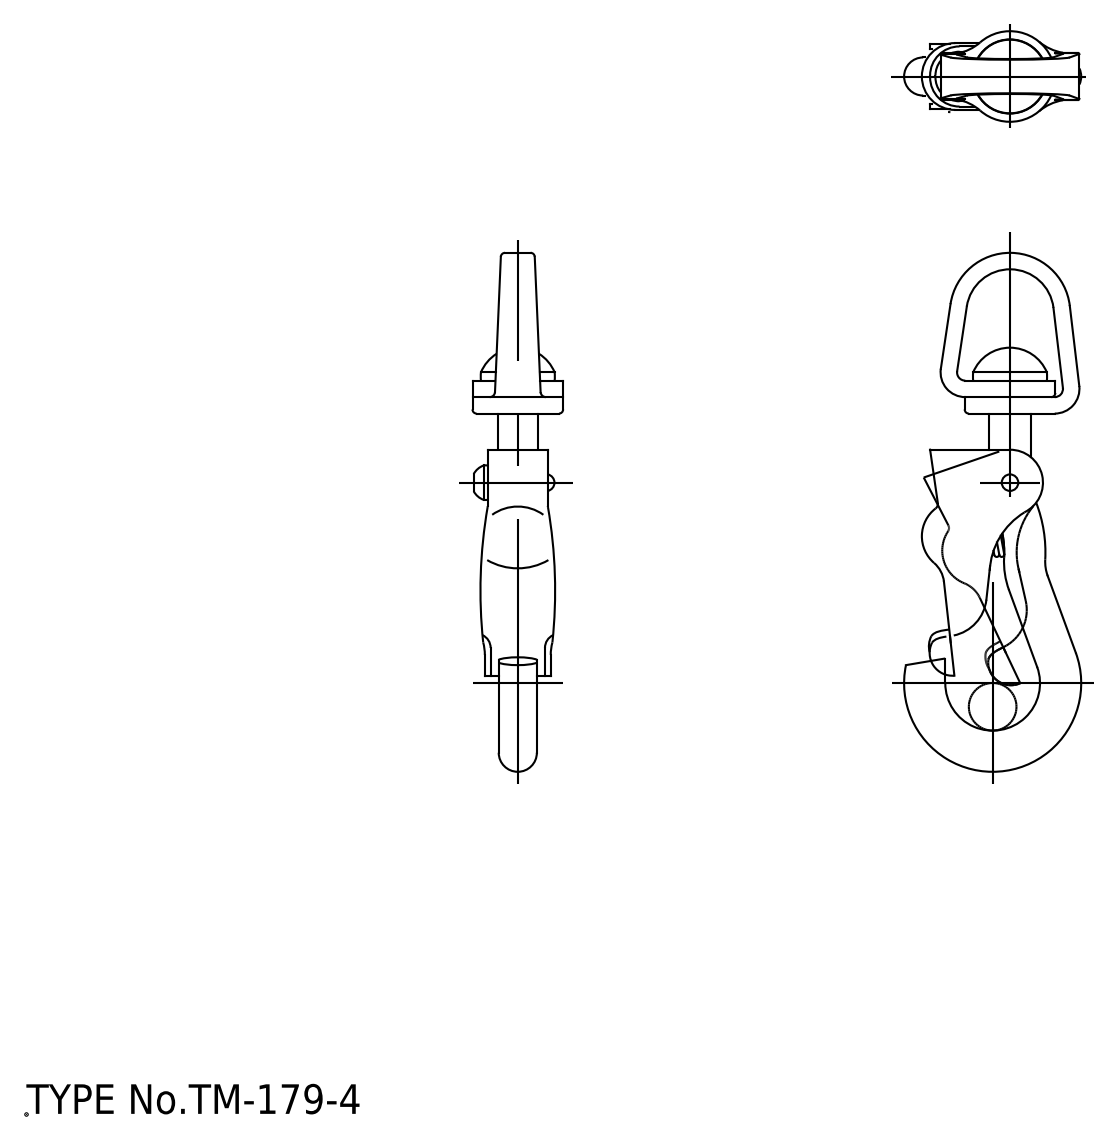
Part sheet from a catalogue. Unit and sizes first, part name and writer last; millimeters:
Units: millimetres
Overall size (bounding box): 49 × 16.72 × 8.56
Round holes (diameter × count): ⌀1.56 ×1, ⌀4.5 ×1
Round bosses / shafts (diameter × count): ⌀8.56 ×1
Partial cylindrical surfaces — rounded edges, fillets, slot ends (radius × count): R1.8 ×5, R0.5 ×3, R0.54 ×3, R1.04 ×3, R0.39 ×2, R0.78 ×2, R2.25 ×2, R2.33 ×2
Main face-to-face distances: 0.5, 5.18, 1.55, 3.11, 4.68, 5.68, 0.54, 1.04, 4.64, 4.14
Volume: 1 171 mm³ · Surface area: 2 039 mm²
Bodies: 3 solids, 160 faces (43 planar, 64 cylindrical, 53 other)
Part name (STEP PRODUCT): Dカン; フック; レバー
STEP written by: spGate 20.6.3 (****-****-****-****) (AUTOMOTIVE_DESIGN)
